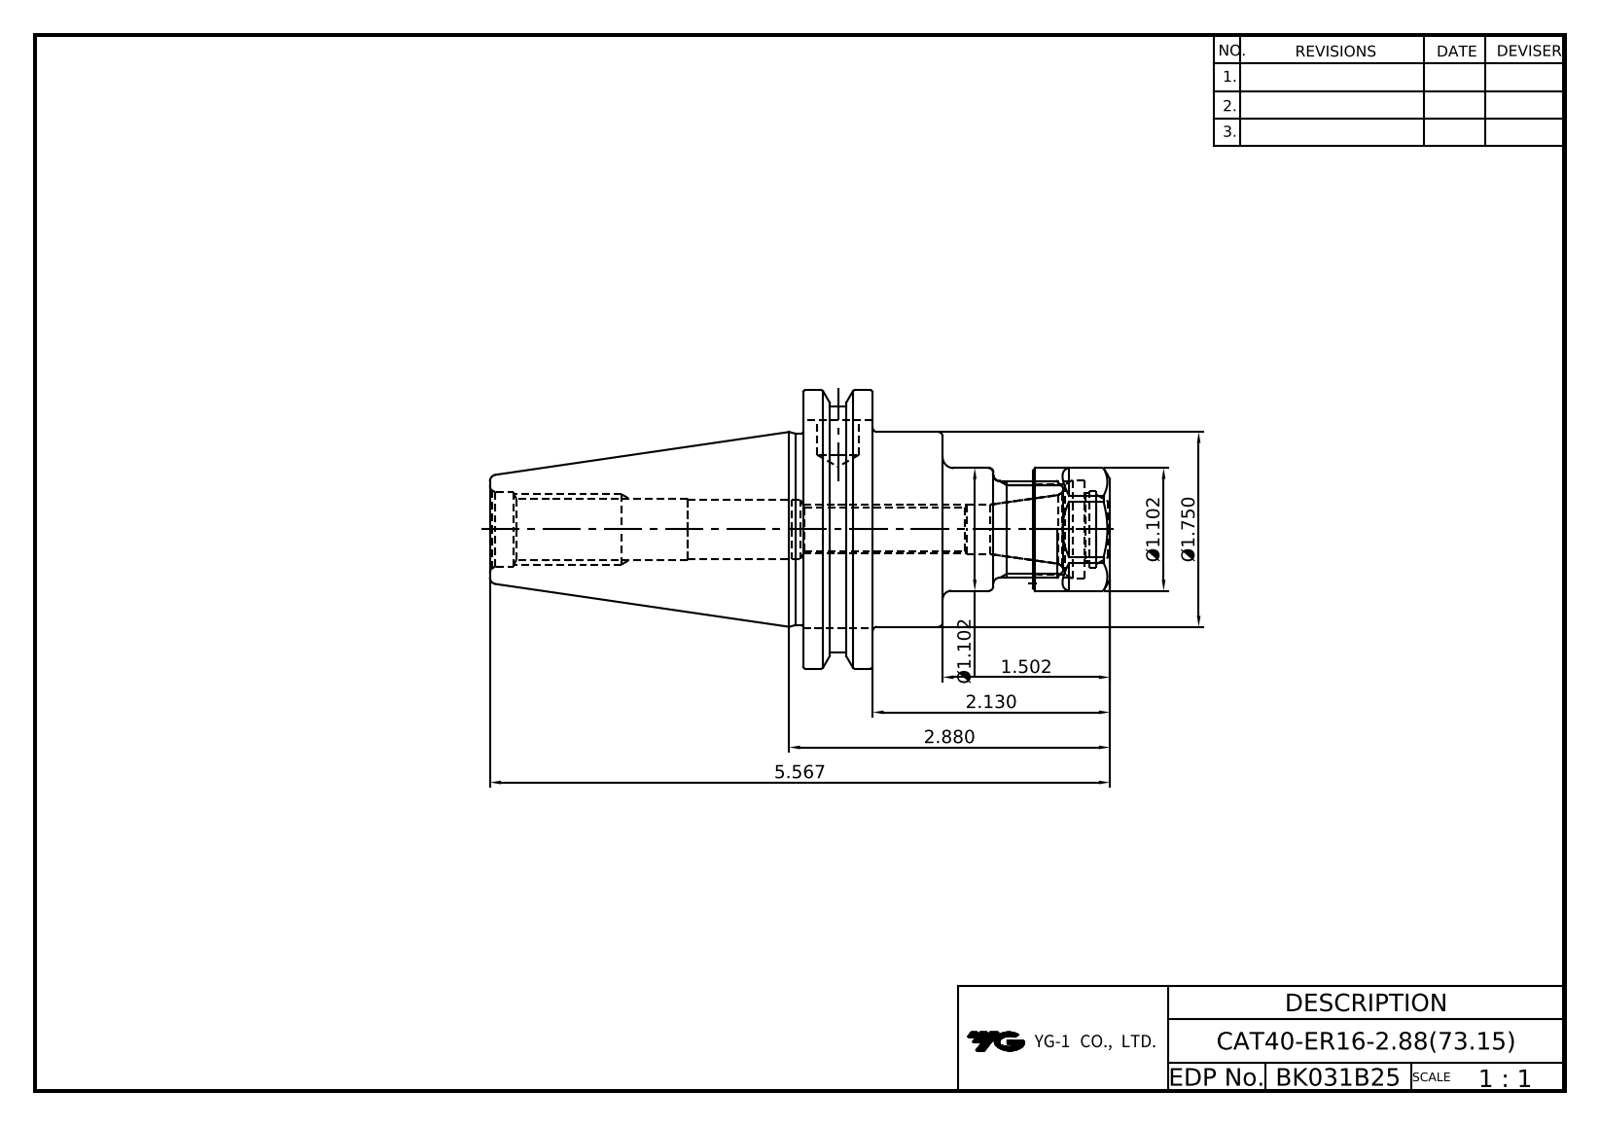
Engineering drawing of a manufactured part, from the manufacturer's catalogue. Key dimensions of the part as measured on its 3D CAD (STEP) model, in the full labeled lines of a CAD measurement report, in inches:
Part name (STEP PRODUCT): LO-CAT40-ER16-73.15; ER16NUT
STEP written by: Autodesk Inventor 2025 (AUTOMOTIVE_DESIGN)
Units: inches
Bodies: 2 solids, 95 faces (49 planar, 24 cylindrical, 22 other)
Overall size (bounding box): 5.567 × 2.5 × 2.405
Volume: 8.558 in³ · Surface area: 46.34 in²
Round holes (diameter × count): ⌀0.039 ×1, ⌀0.37 ×1, ⌀0.375 ×1, ⌀0.445 ×1, ⌀0.504 ×1, ⌀0.527 ×1, ⌀0.642 ×1, ⌀0.697 ×1, ⌀0.811 ×1, ⌀0.886 ×1
Round bosses / shafts (diameter × count): ⌀2.5 ×1, ⌀2.217 ×1, ⌀1.75 ×1, ⌀1.717 ×1, ⌀1.102 ×1, ⌀0.866 ×1
Partial cylindrical surfaces — rounded edges, fillets, slot ends (radius × count): R0.303 ×2
Main face-to-face distances: 0.625, 1.253, 0.628, 2.755, 2.13, 1.502, 0.189, 1.708, 1.083, 0.455
Hole centre spacings: 0.472
